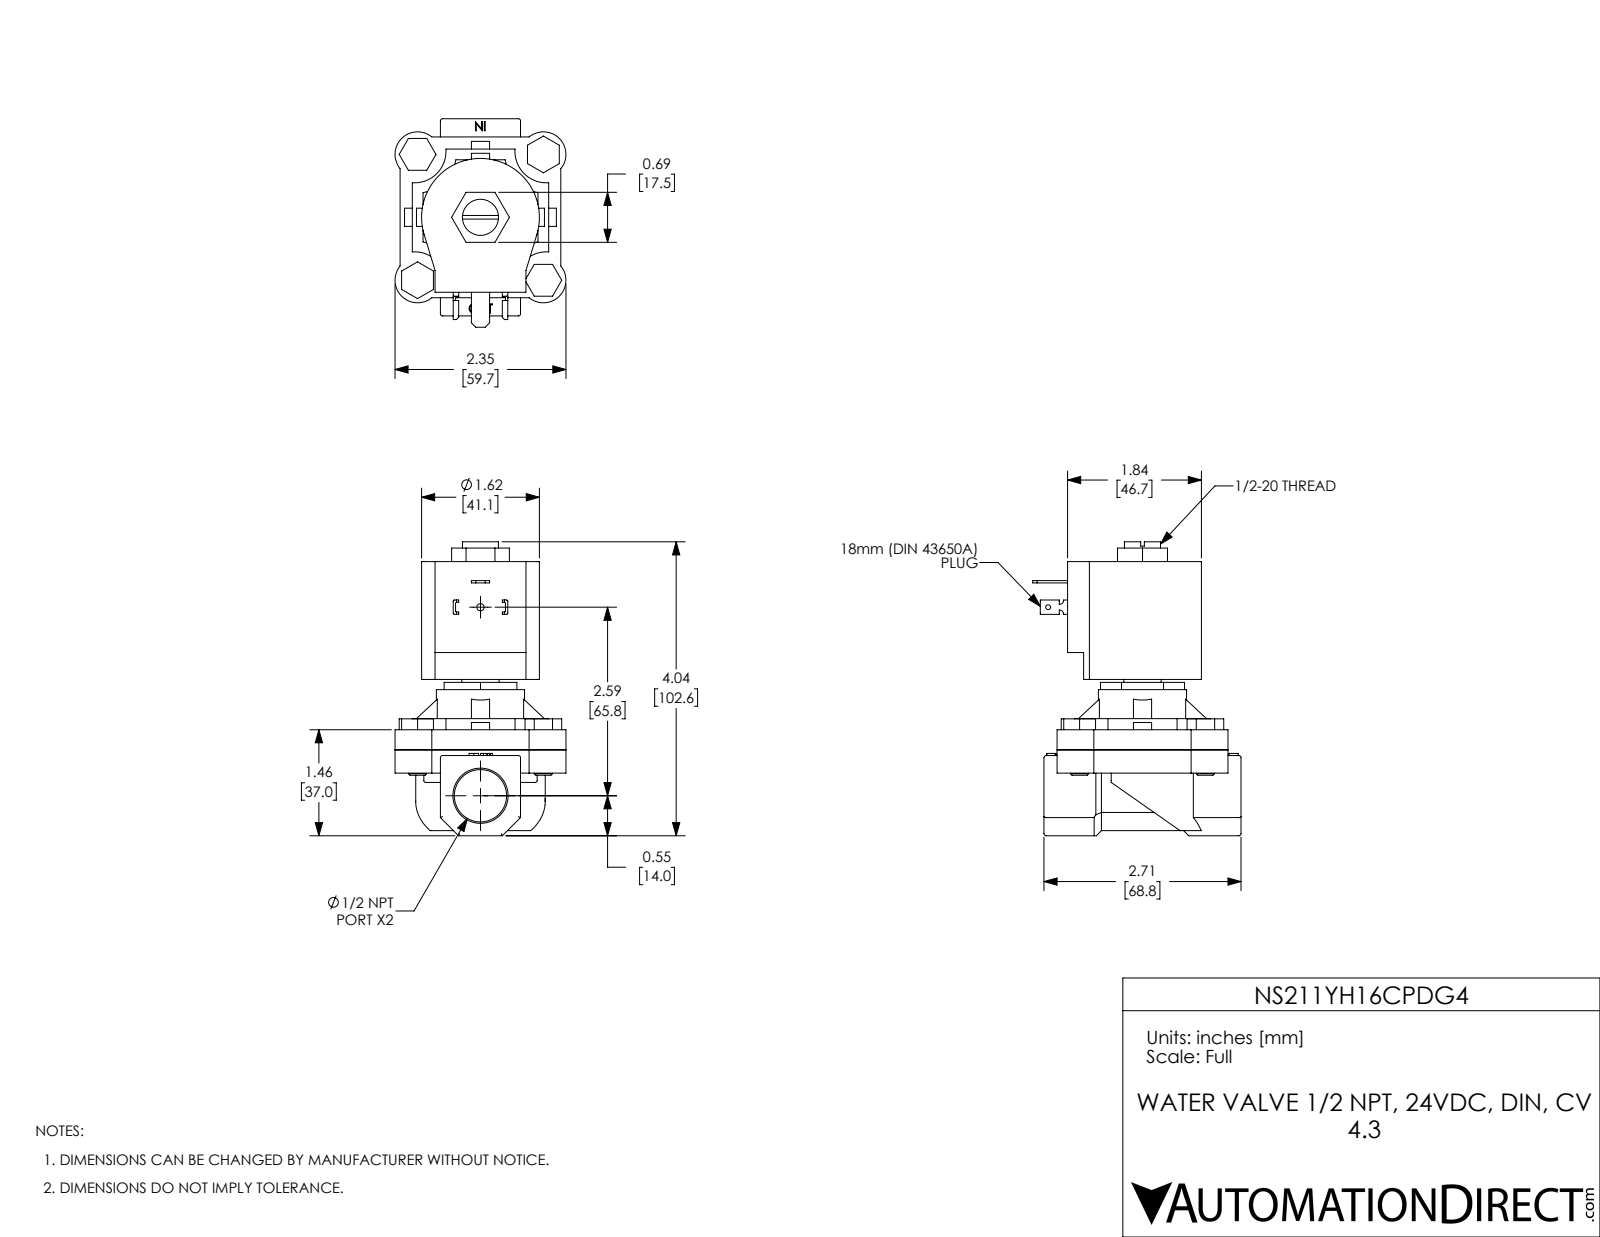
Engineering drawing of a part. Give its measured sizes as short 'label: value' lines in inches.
name: NS211YH16CPDG4
written by: SolidWorks 2024 (CONFIG_CONTROL_DESIGN)
unit: in
bodies: 11 solids, 385 faces (239 planar, 113 cylindrical, 33 other)
size: 4.04 × 2.865 × 2.35
volume: 10.1 in³; area: 67.71 in²
holes: 4× ⌀0.25, 1× ⌀0.067, 1× ⌀0.1, 1× ⌀0.496, 1× ⌀0.512, 1× ⌀0.719, 1× ⌀1.155
bosses: 4× ⌀0.248, 1× ⌀1.213
rounds: 15× R0.03, 8× R0.015, 4× R0.31, 4× R0.432, 4× R0.579, 2× R0.06, 1× R0.81, 1× R0.89
face distances: 0.276, 2.587, 2.311, 0.32, 0.596, 2.907, 0.554, 1.656, 0.25, 2.21
hole spacings: 1.223, 1.73, 2.446, 2.591
